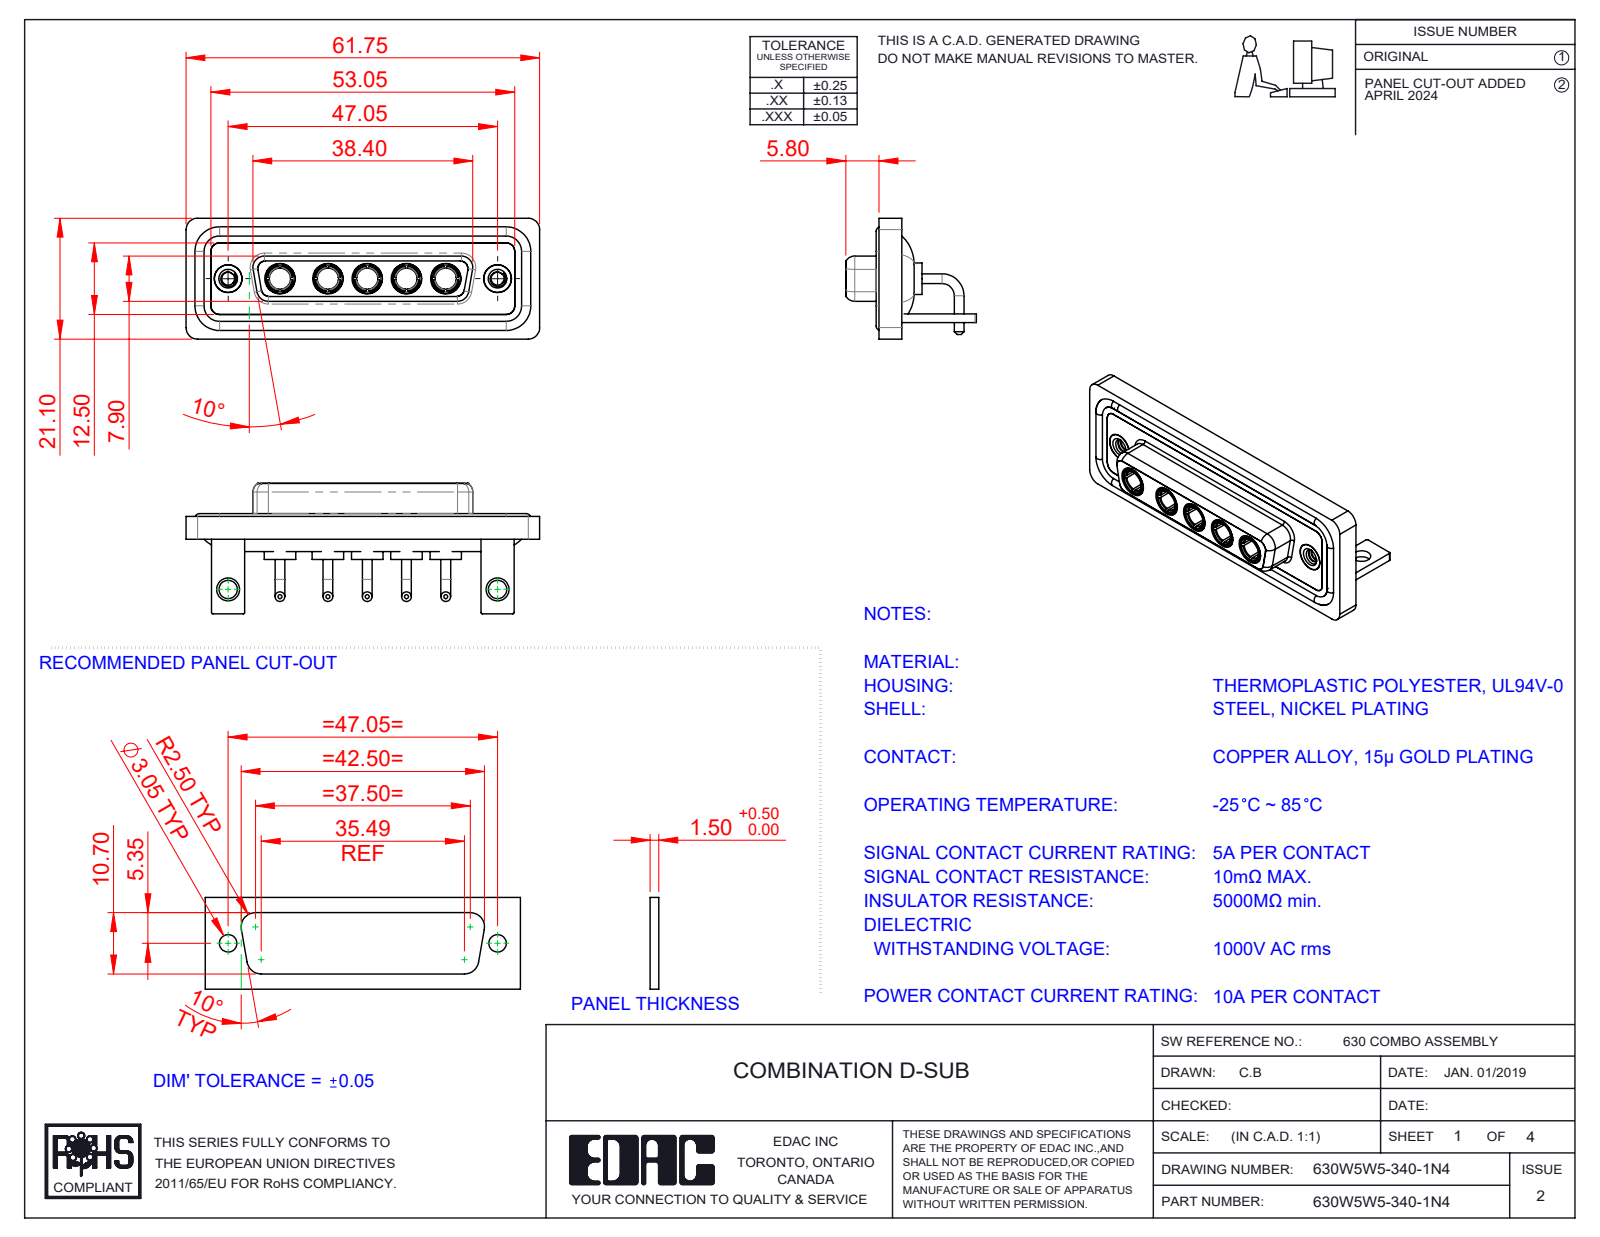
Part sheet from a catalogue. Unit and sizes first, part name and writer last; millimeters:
Units: millimetres
Overall size (bounding box): 61.75 × 22.8 × 21.1
Round holes (diameter × count): ⌀4.85 ×7, ⌀3.7 ×5, ⌀5.3 ×5, ⌀2.26 ×2, ⌀3.2 ×2, ⌀4 ×2, ⌀4.05 ×2, ⌀5 ×2
Round bosses / shafts (diameter × count): ⌀1.7 ×10, ⌀5.5 ×5, ⌀5.2 ×5, ⌀4.96 ×5, ⌀4.75 ×5, ⌀3.75 ×5, ⌀1.6 ×4, ⌀4.95 ×2
Partial cylindrical surfaces — rounded edges, fillets, slot ends (radius × count): R2 ×19, R1.5 ×18, R0.25 ×16, R1.35 ×8, R1.6 ×8, R0.5 ×5, R2.1 ×5, R0.6 ×4
Main face-to-face distances: 0.4, 1.8, 1.5, 2.9, 3.7, 4.1, 1.1, 1.4, 1.6, 2.5
Hole centre spacings: 6.86, 9.04, 38.01, 47.05, 6.87, 8.38, 13.72, 13.73
Volume: 8 513 mm³ · Surface area: 14 295 mm²
Bodies: 19 solids, 824 faces (270 planar, 337 cylindrical, 217 other)
Part name (STEP PRODUCT): 630Combo Housing_5W5; 630Combo Stabilizer Bracket_50 Contacts; 630Combo Shell Front_25 Contacts; 630Combo Threaded Rivet_2 (+4 more)
STEP written by: SolidWorks 2023 (CONFIG_CONTROL_DESIGN)
